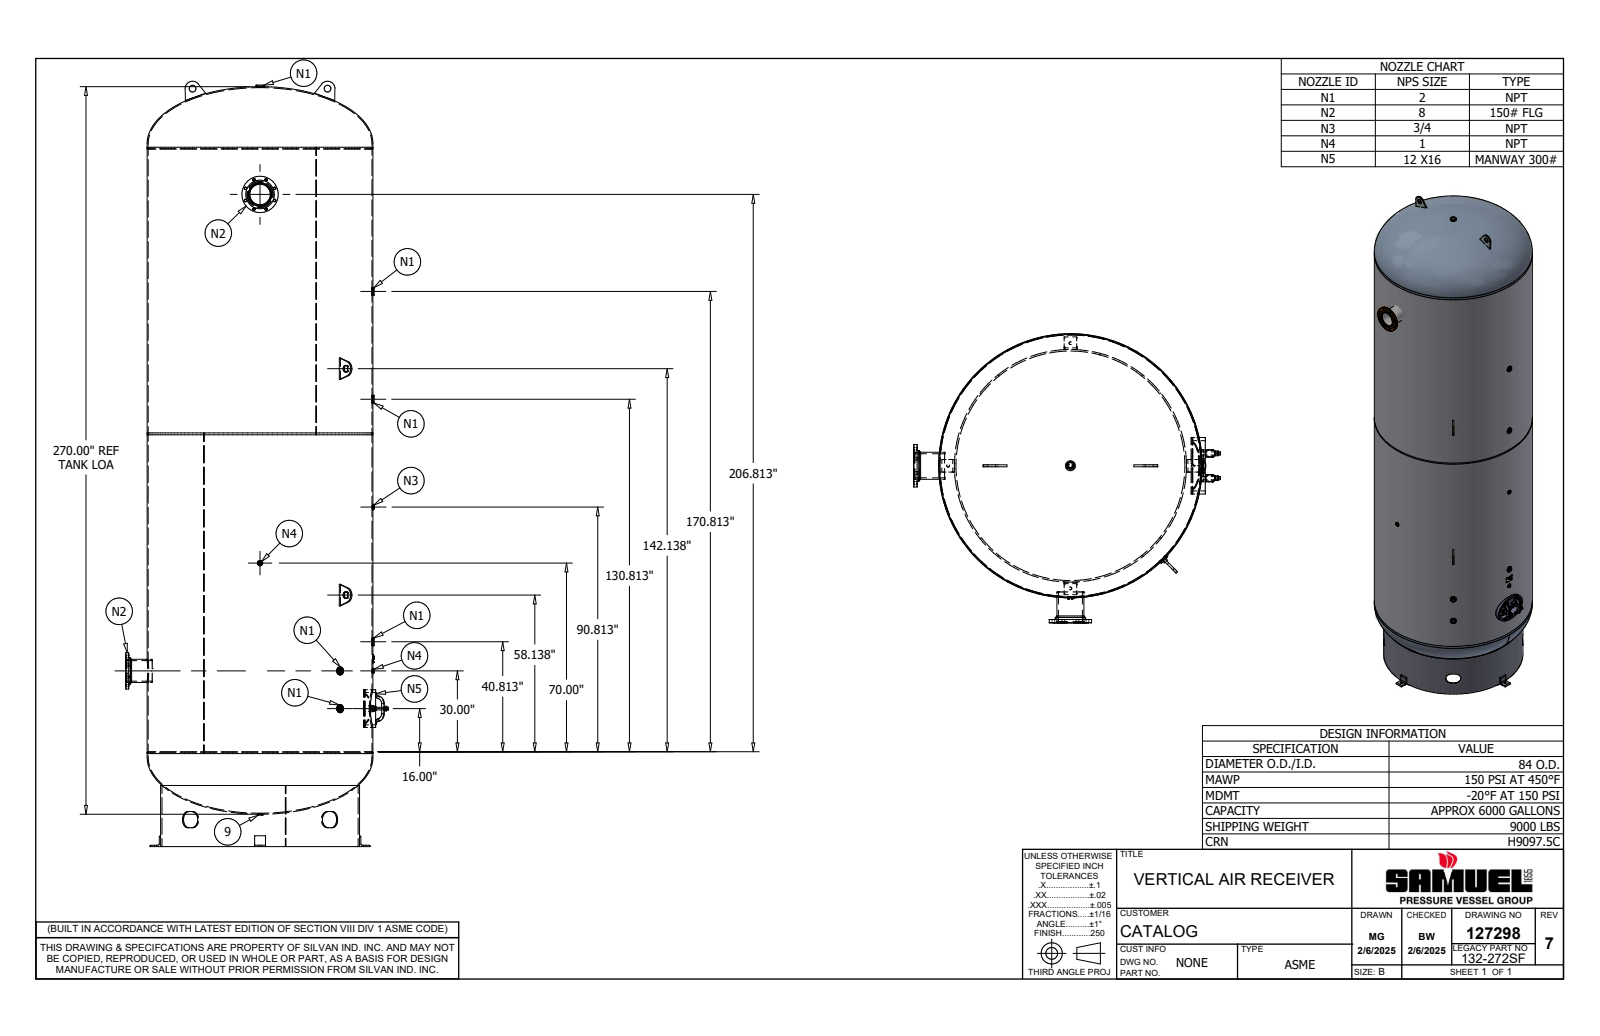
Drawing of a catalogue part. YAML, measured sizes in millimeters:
part_name: "127298; 127300; 150034; 115603 (+8 more)"
step_written_by: "Autodesk Inventor 2022 (AUTOMOTIVE_DESIGN)"
units: millimeters
bodies: {solids: 56, faces: 1097, planar: 503, cylindrical: 226, other: 368}
overall_size: [7213.7, 2484.5, 2336.8]
volume: 519800000
surface_area: 106800000
round_holes:
  - {diameter: 22.2, count: 20}
  - {diameter: 50.8, count: 5}
  - {diameter: 55.2, count: 5}
  - {diameter: 9.5, count: 4}
  - {diameter: 63.5, count: 4}
  - {diameter: 30.3, count: 3}
  - {diameter: 22, count: 2}
  - {diameter: 25.4, count: 2}
  - {diameter: 28.6, count: 2}
  - {diameter: 193.7, count: 2}
  - {diameter: 203.2, count: 2}
  - {diameter: 219.1, count: 2}
round_bosses_or_shafts:
  - {diameter: 76.2, count: 5}
  - {diameter: 66.7, count: 5}
  - {diameter: 50.8, count: 3}
  - {diameter: 39.7, count: 3}
  - {diameter: 342.9, count: 2}
  - {diameter: 269.9, count: 2}
  - {diameter: 246.1, count: 2}
  - {diameter: 25.4, count: 2}
partial_cylinders:
  - {radius: 12.7, count: 12}
  - {radius: 19.7, count: 12}
  - {radius: 9.5, count: 10}
  - {radius: 76.2, count: 7}
  - {radius: 25.4, count: 6}
  - {radius: 19.1, count: 4}
  - {radius: 29.4, count: 4}
  - {radius: 69.9, count: 4}
face_to_face_distances: [15.9, 12.7, 576.3, 17.4, 3898.9, 3322.7, 876.3, 3881.5, 6591.3, 300.1]
hole_center_spacings: [149.2, 275.7, 211, 114.2, 114.2, 298.5, 211, 355.6]
